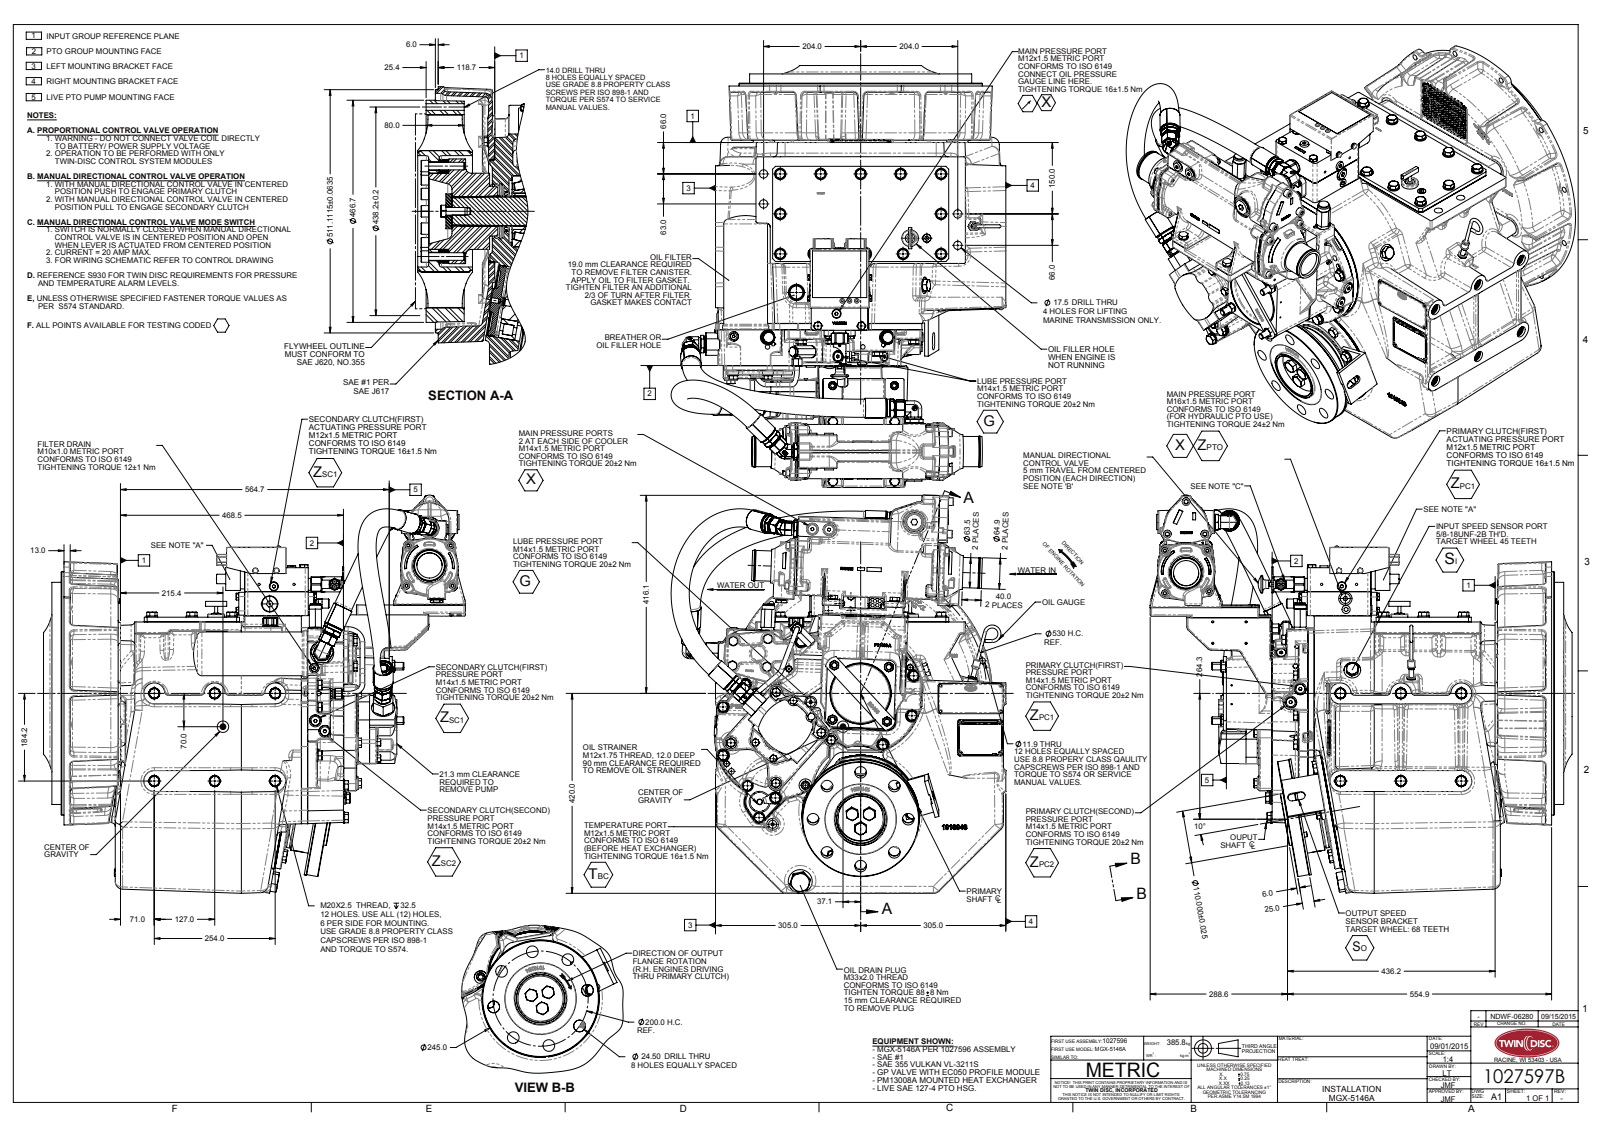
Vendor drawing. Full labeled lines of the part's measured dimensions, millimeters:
Part name (STEP PRODUCT): 1027597B
STEP written by: SolidWorks 2010 (AUTOMOTIVE_DESIGN)
Units: millimetres
Bodies: 0 solids, 11302 faces (6759 planar, 2054 cylindrical, 2489 other)
Overall size (bounding box): 886.51 × 836.76 × 706.05
Round holes (diameter × count): ⌀7 ×79, ⌀11.91 ×12, ⌀25 ×10, ⌀14 ×8, ⌀24.5 ×8, ⌀8.8 ×6, ⌀10 ×6, ⌀23.51 ×6, ⌀6.75 ×5, ⌀7.71 ×5, ⌀12 ×5, ⌀4.2 ×4
Round bosses / shafts (diameter × count): ⌀24 ×40, ⌀19.85 ×8, ⌀13 ×8, ⌀18.9 ×7, ⌀38.1 ×6, ⌀16 ×6, ⌀31.8 ×5, ⌀12 ×5
Partial cylindrical surfaces — rounded edges, fillets, slot ends (radius × count): R4 ×133, R3 ×96, R2 ×74, R2.5 ×72, R8 ×67, R6.5 ×47, R10 ×35, R16 ×32
Main face-to-face distances: 0.39, 13.09, 404.48, 404.09, 13.48, 391, 398.38, 397.99, 384.9, 6.1
Hole centre spacings: 10, 20, 20.07, 459.05, 30, 141.42, 26.51, 34.68
